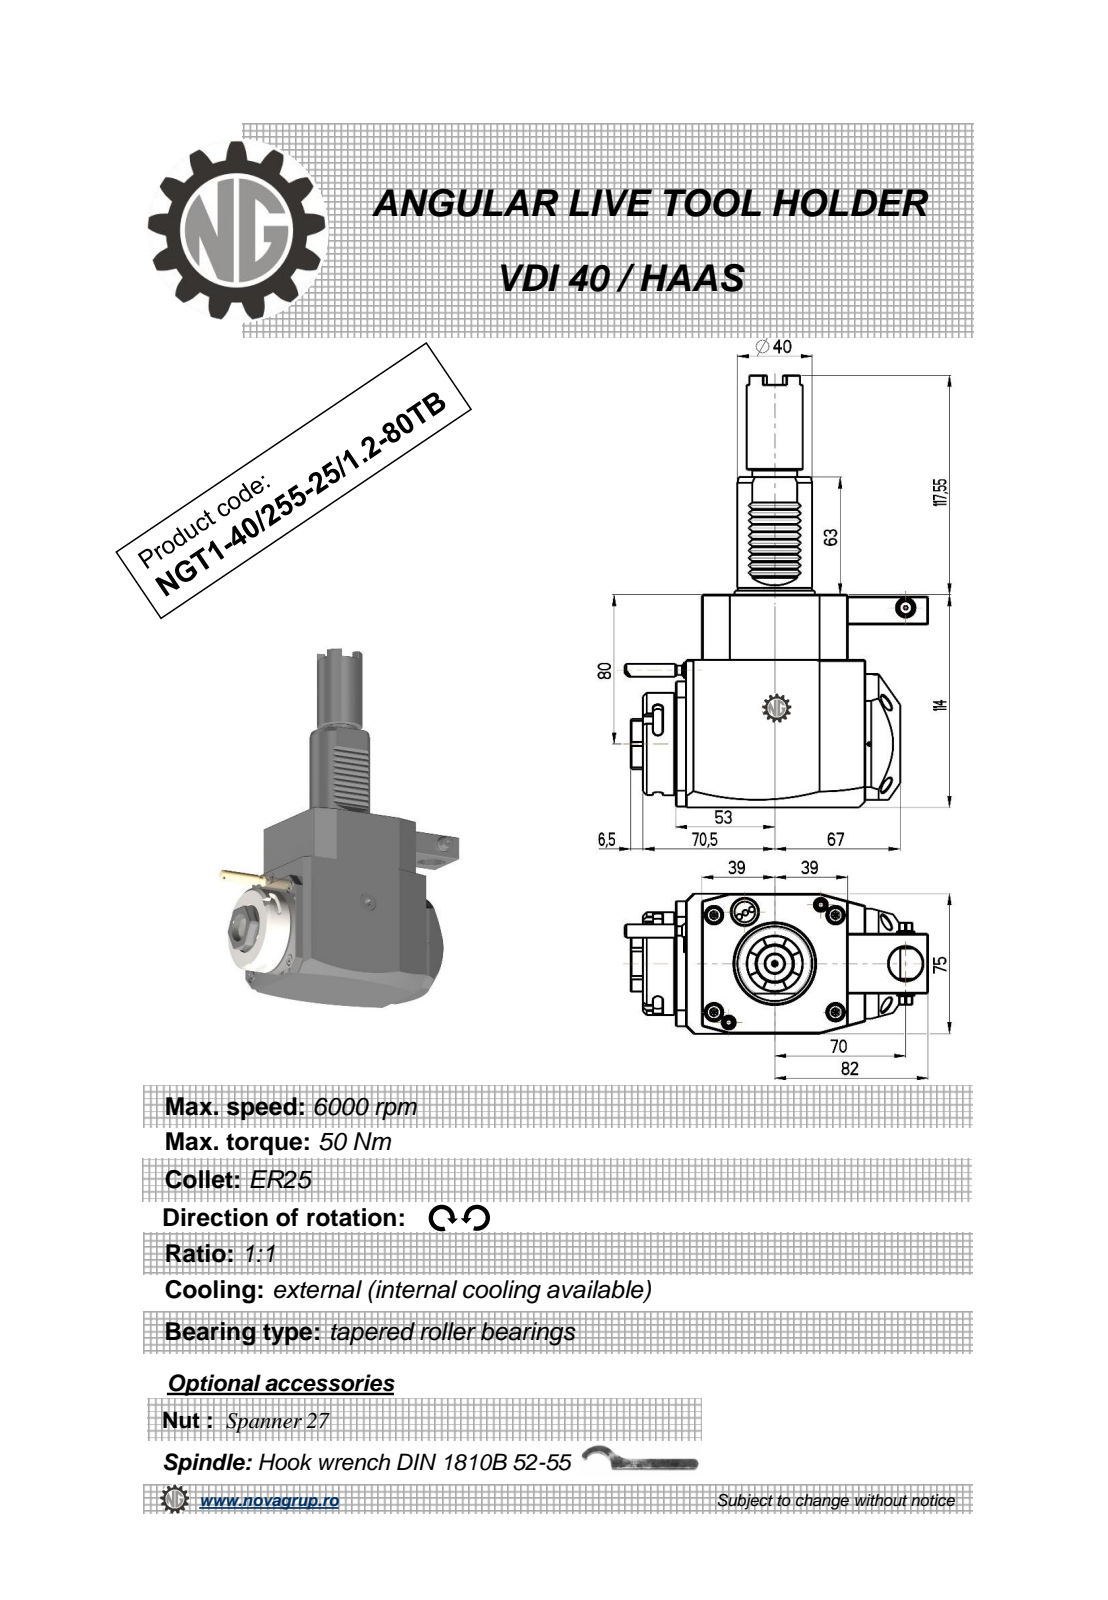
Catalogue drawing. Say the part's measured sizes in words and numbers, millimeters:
The part is named "NGT1_40_255_25_1_2_80TB". Its 3-D file was written by "PRO/ENGINEER BY PARAMETRIC TECHNOLOGY CORPORATION, 2010280 (CONFIG_CONTROL_DESIGN)". It is 1 solid with 393 faces: 213 planar, 92 cylindrical and 88 other. Overall it measures 231.55 by 162.33 by 75 millimeters. Its volume is 998 499 cubic millimeters and its surface area 77 857 square millimeters. Round holes: 2 of diameter 18, 1 of diameter 2, 1 of diameter 2.5, 1 of diameter 3, 1 of diameter 9.5, 1 of diameter 20. Round bosses or shafts: 2 of diameter 8.96, 1 of diameter 55, 1 of diameter 48, 1 of diameter 40, 1 of diameter 30, 1 of diameter 24, 1 of diameter 10, 1 of diameter 7. Partial cylindrical surfaces (rounded edges, fillets, slot ends): 10 of radius 0.3, 6 of radius 2.5, 2 of radius 180, 1 of radius 0.5, 1 of radius 3.85, 1 of radius 4.25, 1 of radius 15, 1 of radius 24.5. The main face-to-face distances are 75, 114, 14, 17.5, 109.5, 79, 92, 78, 31.5, 98. The hole center spacings are 37.35, 43.2, 70, 72.5.
